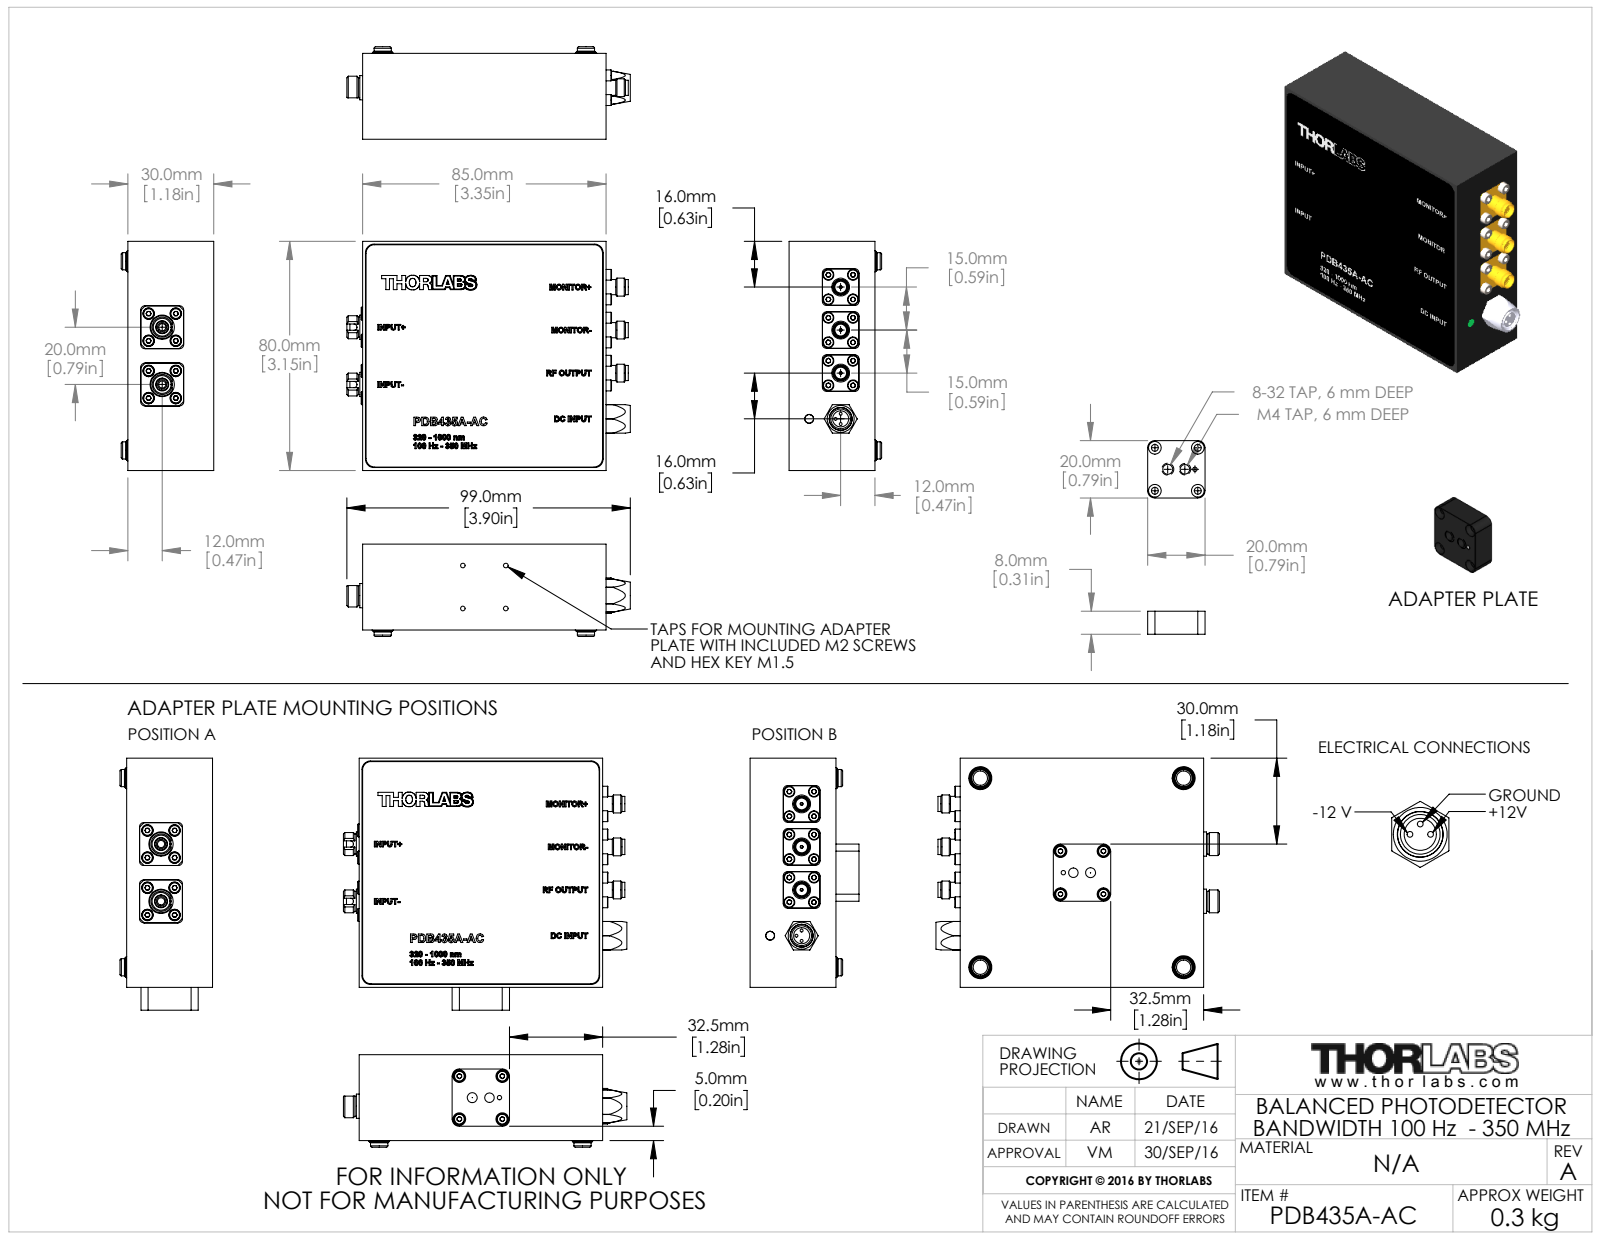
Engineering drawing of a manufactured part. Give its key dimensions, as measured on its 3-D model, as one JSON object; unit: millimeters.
{"part_name": "MTN005462-E0W", "step_written_by": "SolidWorks 2014 (AUTOMOTIVE_DESIGN)", "units": "millimeters", "bodies": {"solids": 90, "faces": 3113, "planar": 1801, "cylindrical": 584, "other": 728}, "overall_size": [99, 88, 38], "volume_mm3": 87719, "surface_area_mm2": 57809, "round_holes": [[1.6, 38], [2.6, 12], [2.2, 8], [2.4, 8], [4, 8], [4.4, 8], [1.02, 6], [8, 5], [0.8, 3], [1, 3], [4.1, 3], [4.2, 3]], "round_bosses_or_shafts": [[3.8, 20], [2, 20], [4.5, 8], [2.5, 8], [0.43, 6], [6, 4], [6.22, 3], [5.3, 3]], "partial_cylinders_radius": [[1.5, 20], [3, 12], [2.5, 8], [5, 8], [1, 4], [9.5, 2], [5.75, 1]], "face_to_face_distances": [29.7, 6, 23.7, 5.5, 80, 2, 74.5, 85, 3.5, 83], "hole_center_spacings": [15, 6.08, 8.6, 9.5, 6.72, 8.75, 11.53, 12.9]}
